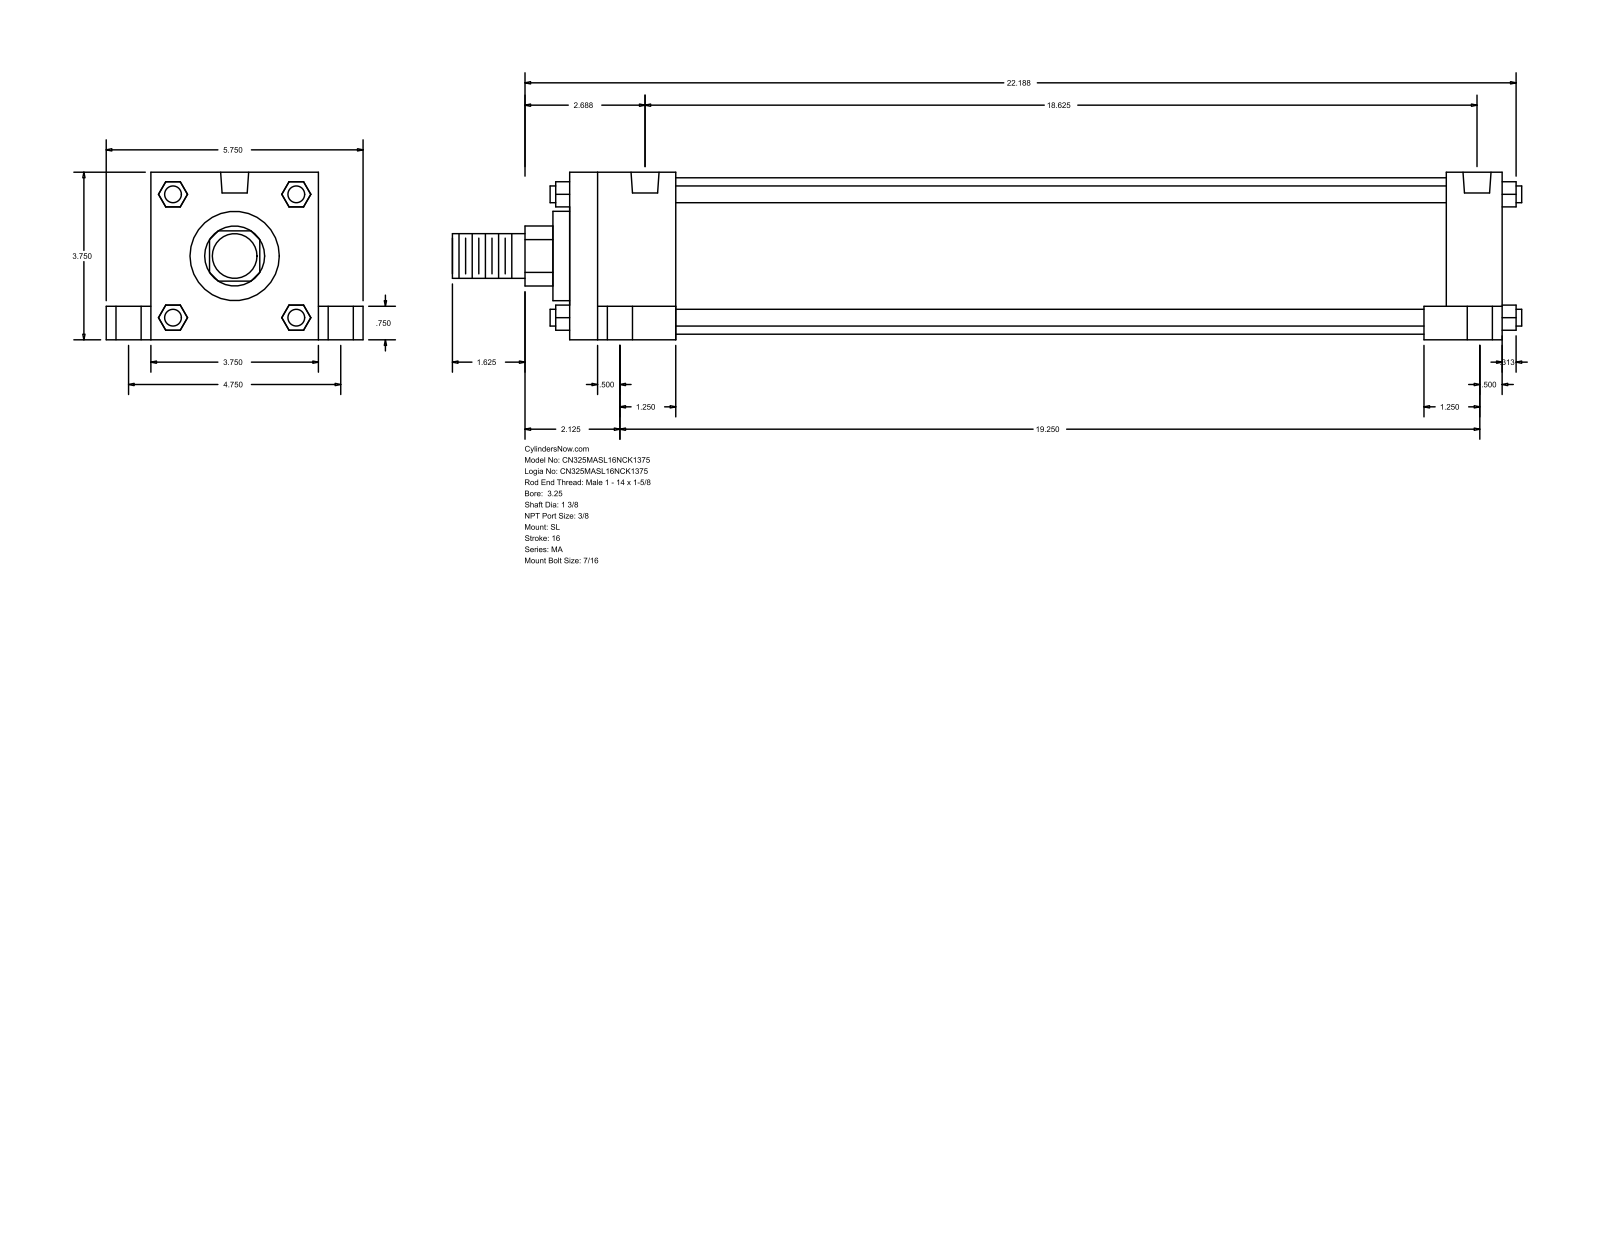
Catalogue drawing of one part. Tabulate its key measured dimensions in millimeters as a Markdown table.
| quantity | value |
| --- | --- |
| part name | MA_SL__0325_1.375 |
| STEP written by | GSSL Pune (CONFIG_CONTROL_DESIGN) |
| units | millimeters |
| bodies | 0 solids, 148 faces (112 planar, 36 cylindrical, 0 other) |
| overall size | 608.01 × 146.05 × 95.25 |
| round holes (diameter × count) | 11.11 × 4, 14.29 × 4, 20.64 × 4, 15.93 × 2 |
| round bosses / shafts (diameter × count) | 9.53 × 4, 88.9 × 1, 50.8 × 1, 34.92 × 1, 25.4 × 1 |
| partial cylindrical surfaces (radius × count) | 17.06 × 1 |
| main face-to-face distances | 95.24, 530.22, 25.41, 120.65, 498.48, 31.74, 60.32, 438.16, 469.9, 19.05 |
| hole center spacings | 60.35, 60.66, 62, 63.27, 120.66, 463.55, 473.75, 478.48 |
